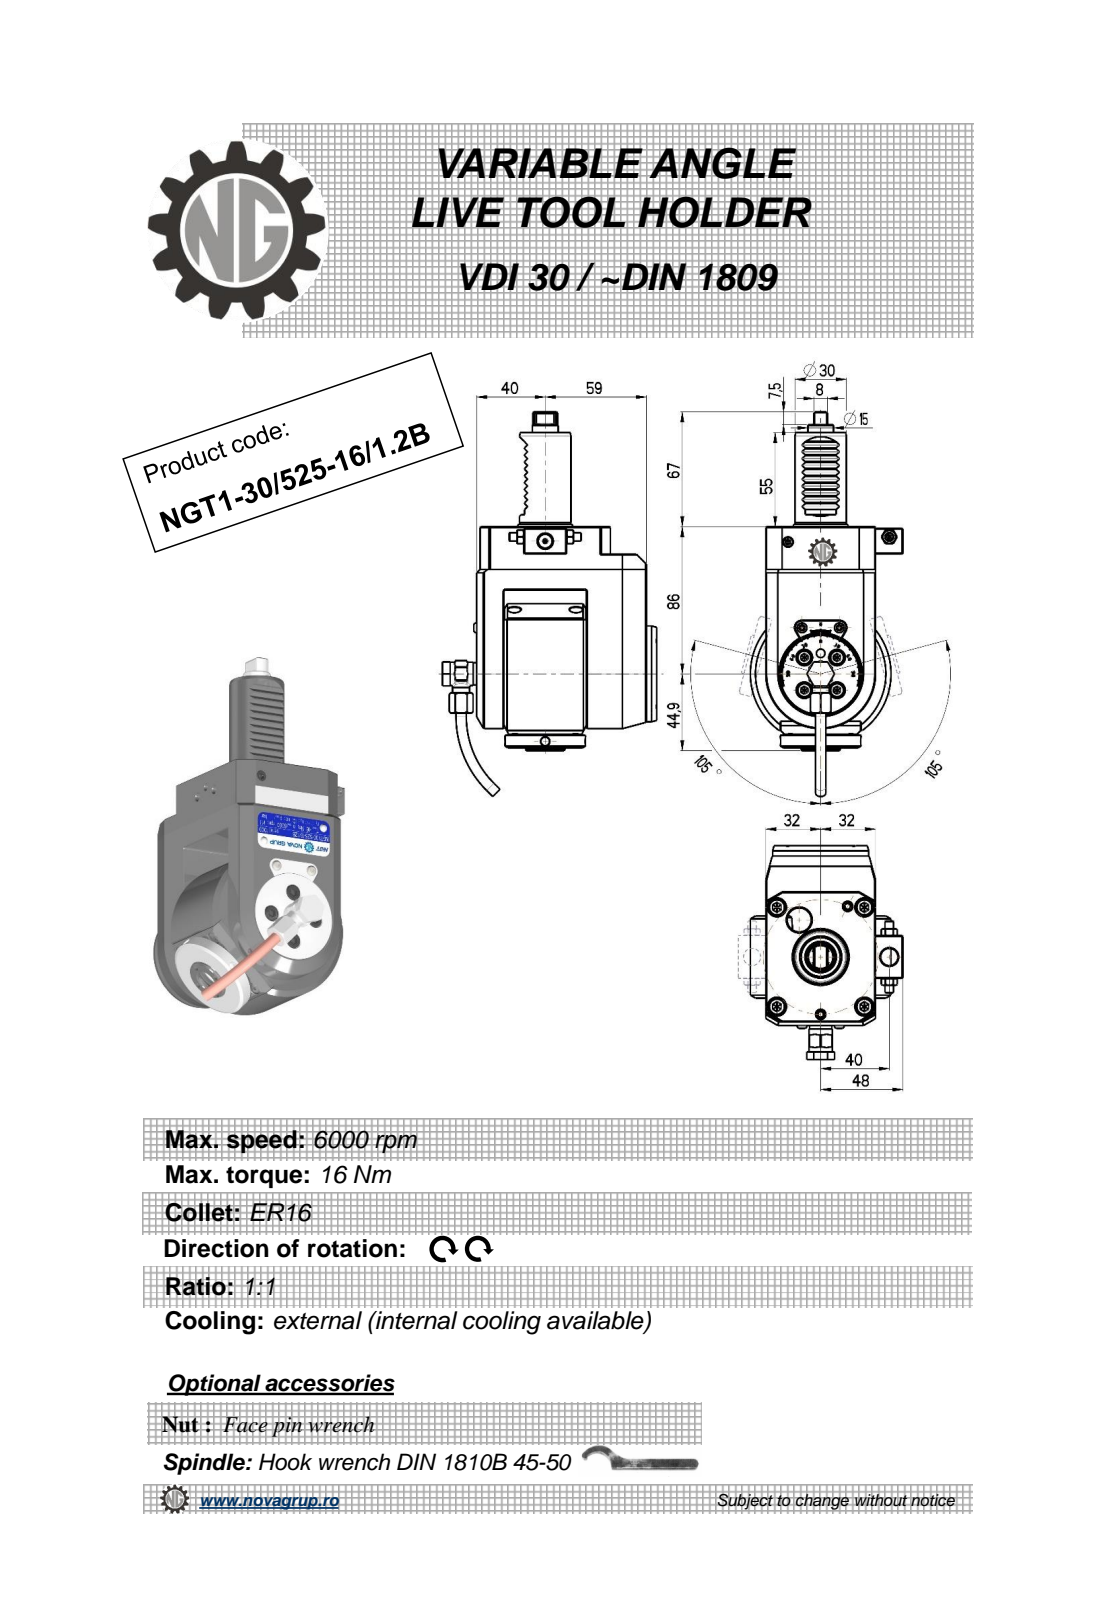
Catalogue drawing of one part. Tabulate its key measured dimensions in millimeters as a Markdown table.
| quantity | value |
| --- | --- |
| part name | NGT1_30_521_16_1_2B |
| STEP written by | PRO/ENGINEER BY PARAMETRIC TECHNOLOGY CORPORATION, 2010280 (CONFIG_CONTROL_DESIGN) |
| units | millimeters |
| bodies | 1 solid, 502 faces (212 planar, 138 cylindrical, 152 other) |
| overall size | 224.67 × 124.9 × 89 |
| volume | 760 250 mm³ |
| surface area | 71 546 mm² |
| round holes (diameter × count) | 3.2 × 4, 4 × 3, 5 × 2, 3 × 1, 4.2 × 1, 6.2 × 1, 9 × 1, 9.5 × 1, 10 × 1, 11 × 1, 12.5 × 1 |
| round bosses / shafts (diameter × count) | 10 × 2, 6 × 2, 5.7 × 2, 82 × 1, 56 × 1, 47 × 1, 35 × 1, 30 × 1 |
| partial cylindrical surfaces (radius × count) | 0.26 × 12, 0.3 × 10, 0.16 × 6, 0.5 × 4, 0.8 × 2, 1 × 2, 7.2 × 1, 7.7 × 1 |
| main face-to-face distances | 64, 16, 37, 99, 6, 105, 83, 21, 14, 35 |
| hole center spacings | 9.25, 13.08, 18.5, 41.06, 49.87, 50.26, 0.4, 30.75 |
